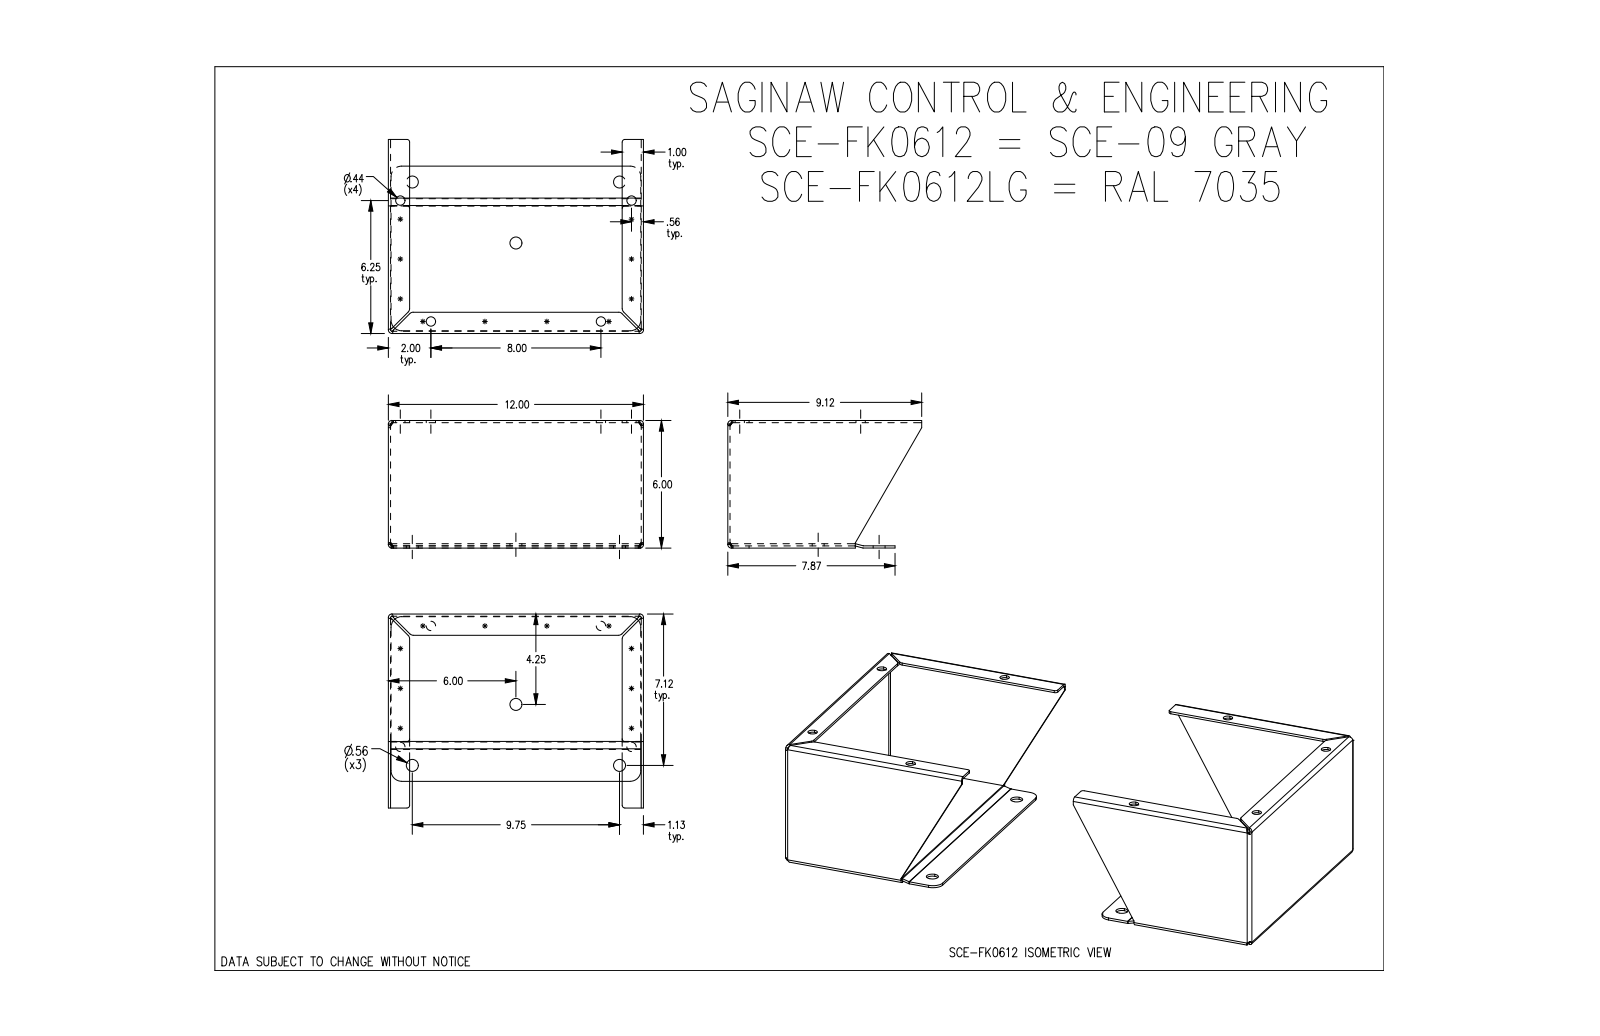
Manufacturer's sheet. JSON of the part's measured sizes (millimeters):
{"part_name": "SCE-FK0612", "step_written_by": "SolidWorks 2019 (CONFIG_CONTROL_DESIGN)", "units": "millimeters", "bodies": {"solids": 4, "faces": 214, "planar": 96, "cylindrical": 86, "other": 32}, "overall_size": [609.6, 304.8, 152.4], "volume_mm3": 995500, "surface_area_mm2": 770300, "round_holes": [[11.1, 8], [14.3, 6]], "partial_cylinders_radius": [[4.2, 16], [1.6, 14], [3.2, 8], [5.6, 8], [12.7, 8], [1.6, 2]], "face_to_face_distances": [2.6, 302.2, 607, 147.1, 304.8, 299.5, 149.8, 2.6, 149.7, 609.6], "hole_center_spacings": [26.3, 138.2, 143.7, 147.1, 149, 168, 270.4, 279.9]}
